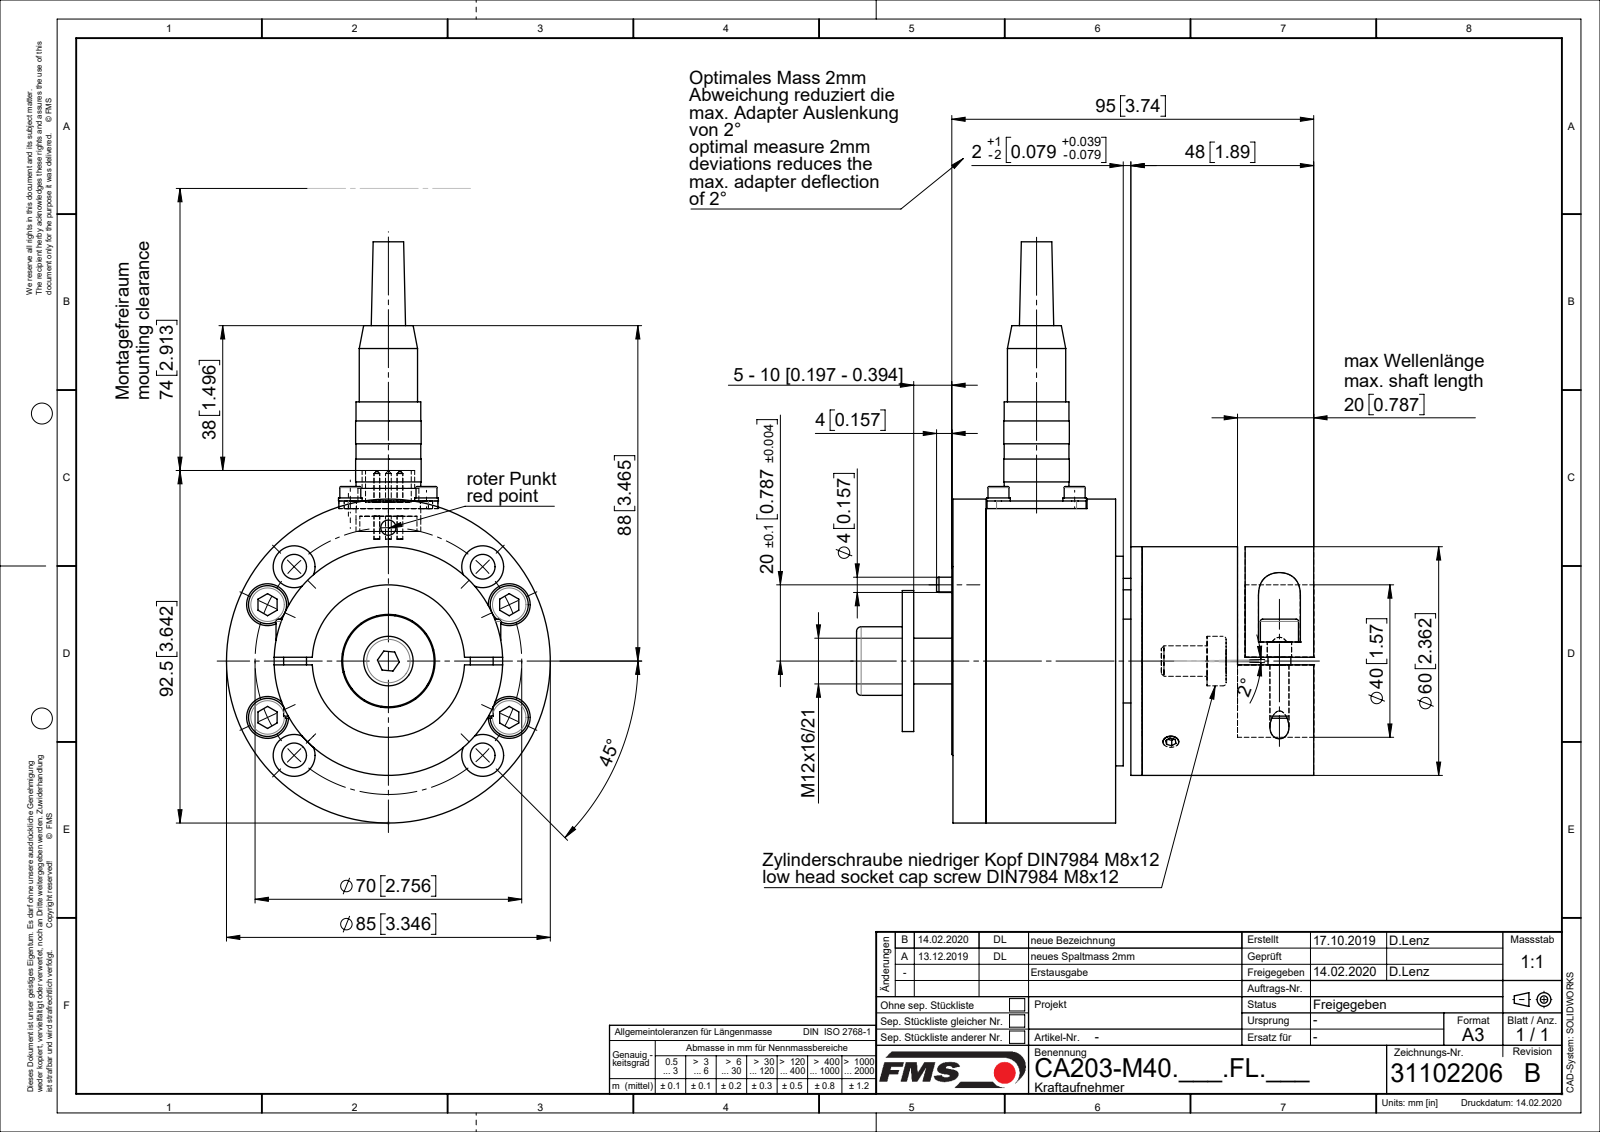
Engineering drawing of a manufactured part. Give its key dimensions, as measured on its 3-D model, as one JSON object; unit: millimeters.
{"part_name": "C0709101_DM40; C0709081; C0612056; C0709072 (+8 more)", "step_written_by": "Mechanical Desktop 2009 (CONFIG_CONTROL_DESIGN)", "units": "millimeters", "bodies": {"solids": 37, "faces": 671, "planar": 221, "cylindrical": 310, "other": 140}, "overall_size": [152.5, 120.5, 85], "volume_mm3": 307089, "surface_area_mm2": 110094, "round_holes": [[2.6, 8], [6.5, 8], [11, 8], [5.15, 6], [3.2, 4], [3.6, 4], [4, 4], [7, 4], [6.4, 2], [3, 1], [4.33, 1], [7.15, 1]], "round_bosses_or_shafts": [[6, 10], [3, 8], [10, 6], [1.5, 5], [6.2, 4], [5.5, 4], [5, 4], [85, 1]], "partial_cylinders_radius": [[2.5, 4], [5, 2], [5.5, 2]], "face_to_face_distances": [45, 49.5, 9, 11.5, 2, 31.5, 10, 43, 1.5, 40.5], "hole_center_spacings": [20, 24.78, 25.2, 32.8, 35, 51.14, 56.46, 28.28]}
